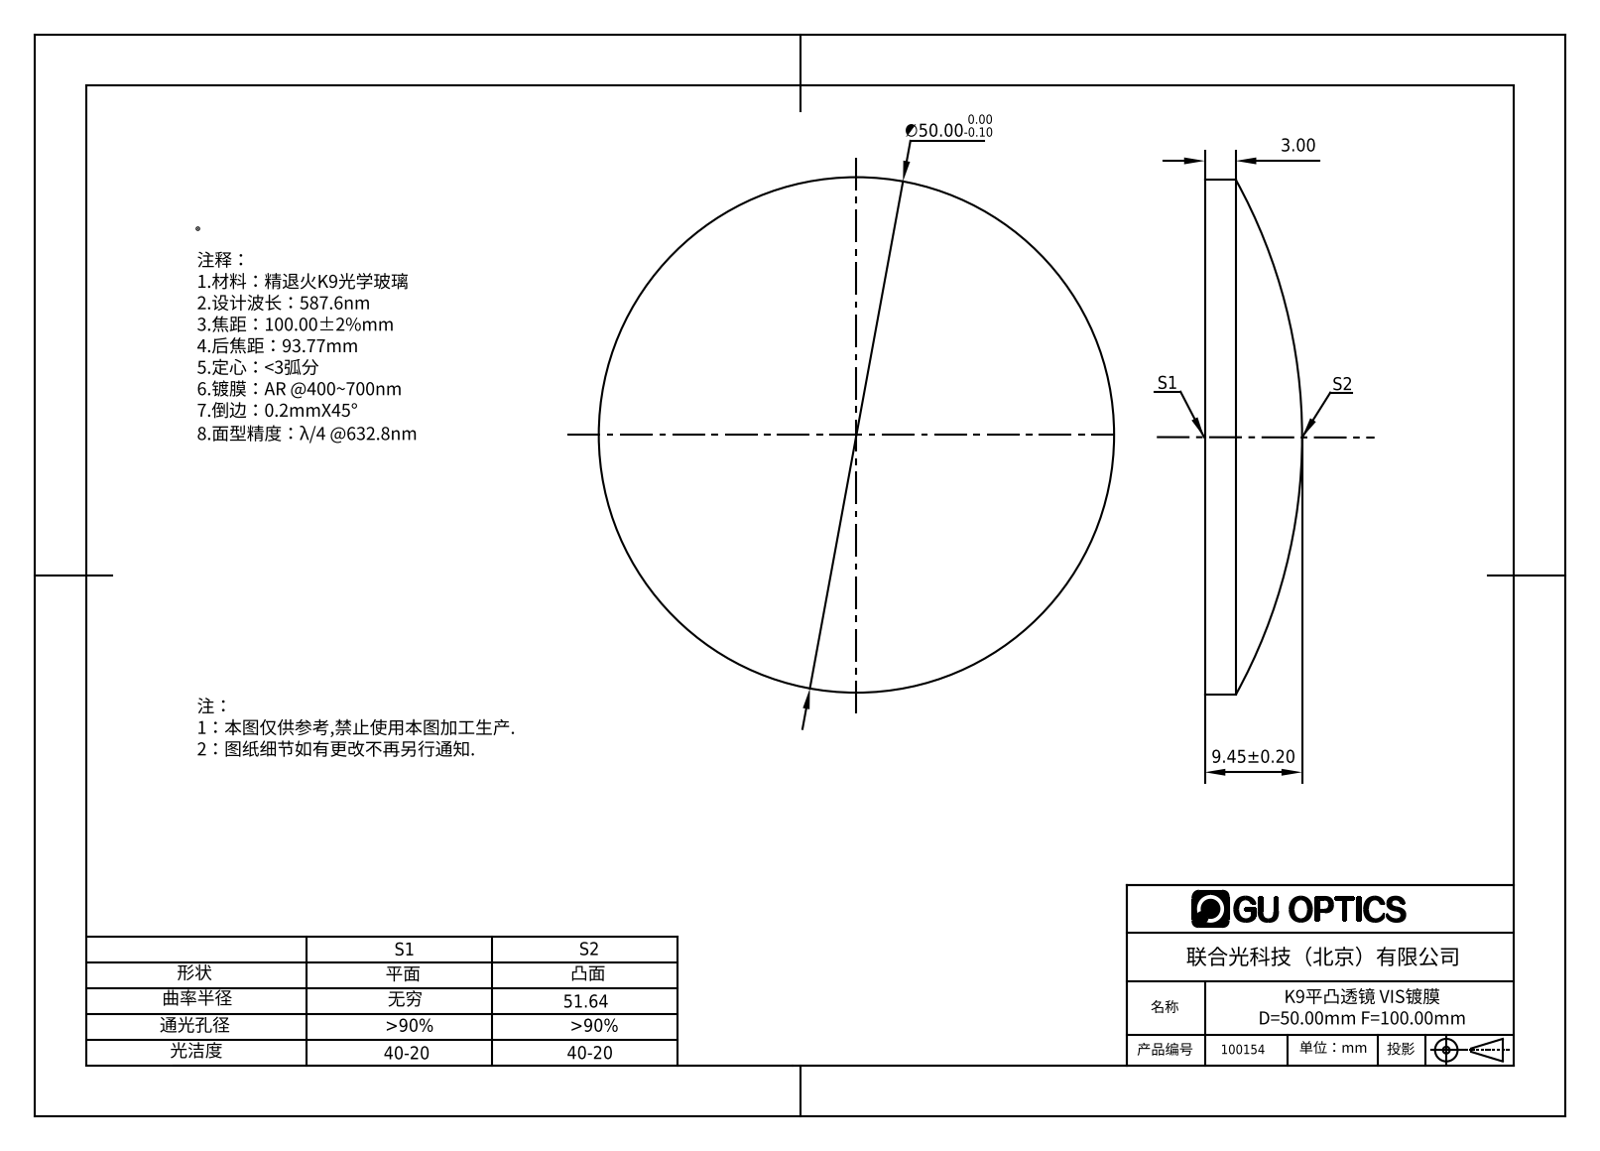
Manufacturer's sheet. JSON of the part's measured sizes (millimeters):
{"part_name": "100154", "step_written_by": "SolidWorks 2016 (AUTOMOTIVE_DESIGN)", "units": "millimeters", "bodies": {"solids": 1, "faces": 6, "planar": 0, "cylindrical": 0, "other": 6}, "overall_size": [50.01, 50.01, 9.55], "volume_mm3": 12372, "surface_area_mm2": 4531}
